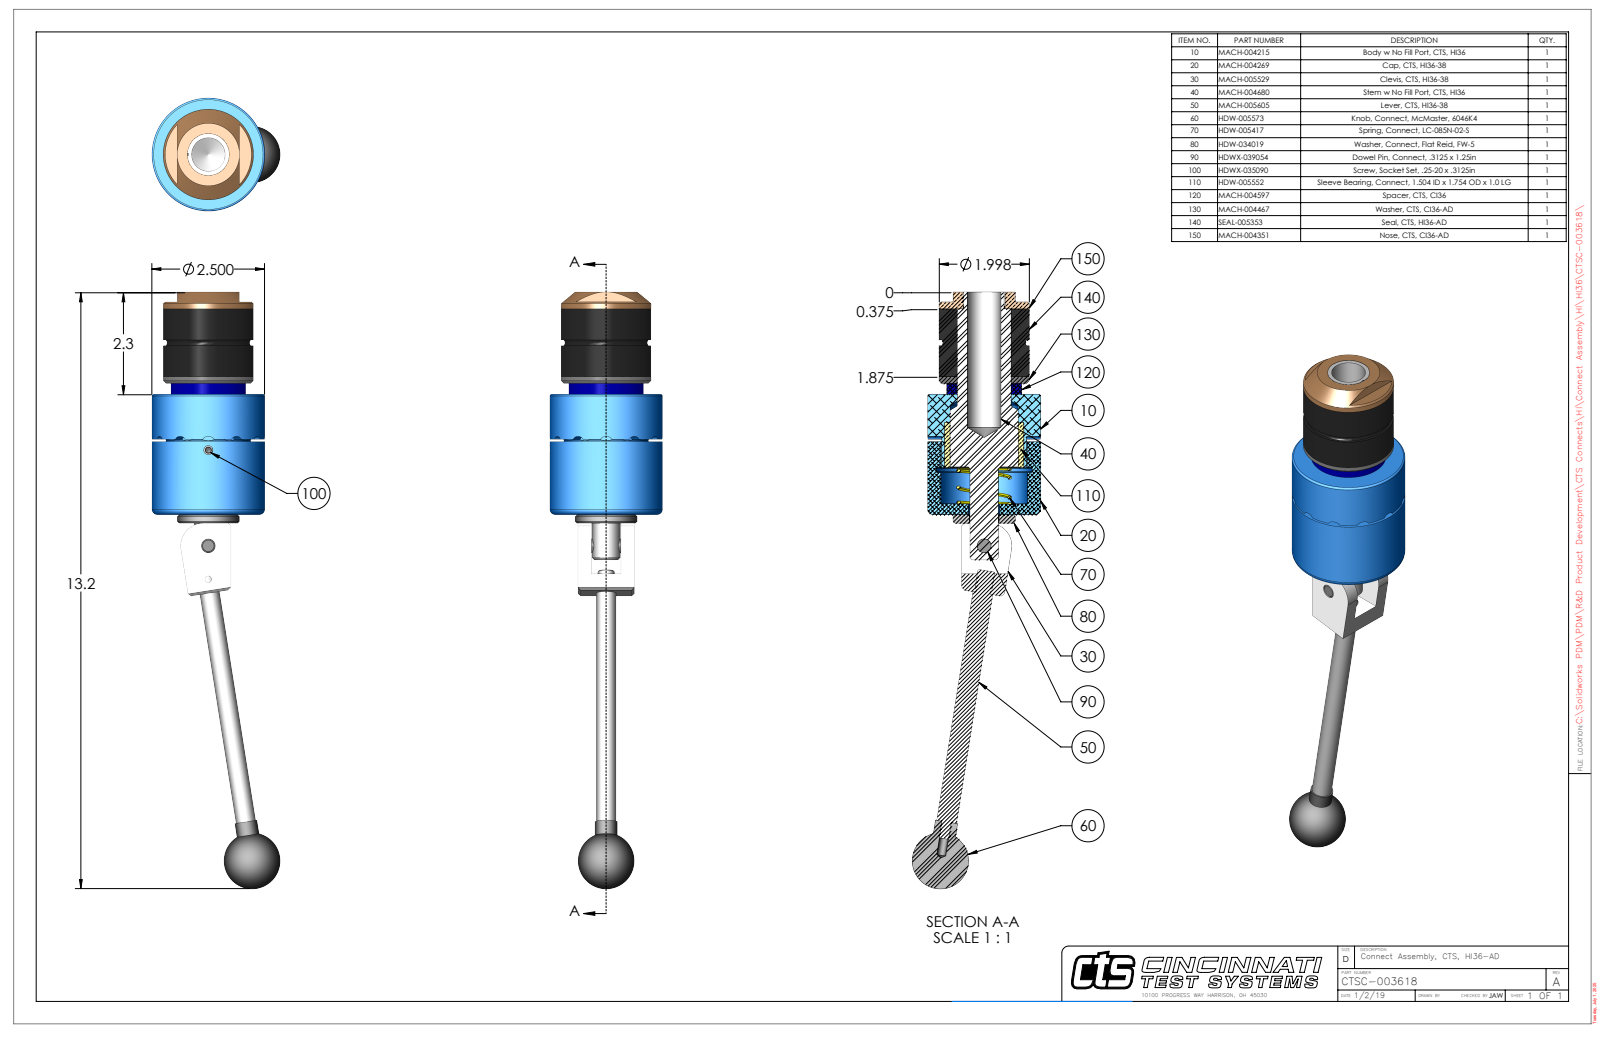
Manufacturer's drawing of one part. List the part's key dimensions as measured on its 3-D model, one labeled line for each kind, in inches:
Part name (STEP PRODUCT): CTSC-003618
STEP written by: SolidWorks 2023 (AUTOMOTIVE_DESIGN)
Units: inches
Bodies: 10 solids, 271 faces (97 planar, 107 cylindrical, 67 other)
Overall size (bounding box): 13.215 × 2.843 × 2.5
Volume: 21.68 in³ · Surface area: 120.3 in²
Round holes (diameter × count): ⌀0.201 ×2, ⌀0.15 ×1, ⌀0.311 ×1, ⌀0.313 ×1, ⌀0.314 ×1, ⌀0.656 ×1, ⌀0.696 ×1, ⌀0.75 ×1, ⌀0.922 ×1, ⌀1.188 ×1, ⌀1.19 ×1, ⌀1.195 ×1
Round bosses / shafts (diameter × count): ⌀2.5 ×1, ⌀1.998 ×1, ⌀1.875 ×1, ⌀1.656 ×1, ⌀1.38 ×1, ⌀1.186 ×1, ⌀1 ×1, ⌀0.904 ×1
Partial cylindrical surfaces — rounded edges, fillets, slot ends (radius × count): R0.12 ×12, R0.029 ×2, R0.5 ×1, R1.188 ×1
Main face-to-face distances: 2.668, 4.555, 1.887, 3.055, 0.387, 1.5, 2.905, 0.237, 0.15, 1.65
Hole centre spacings: 0.74, 2.118, 2.858
